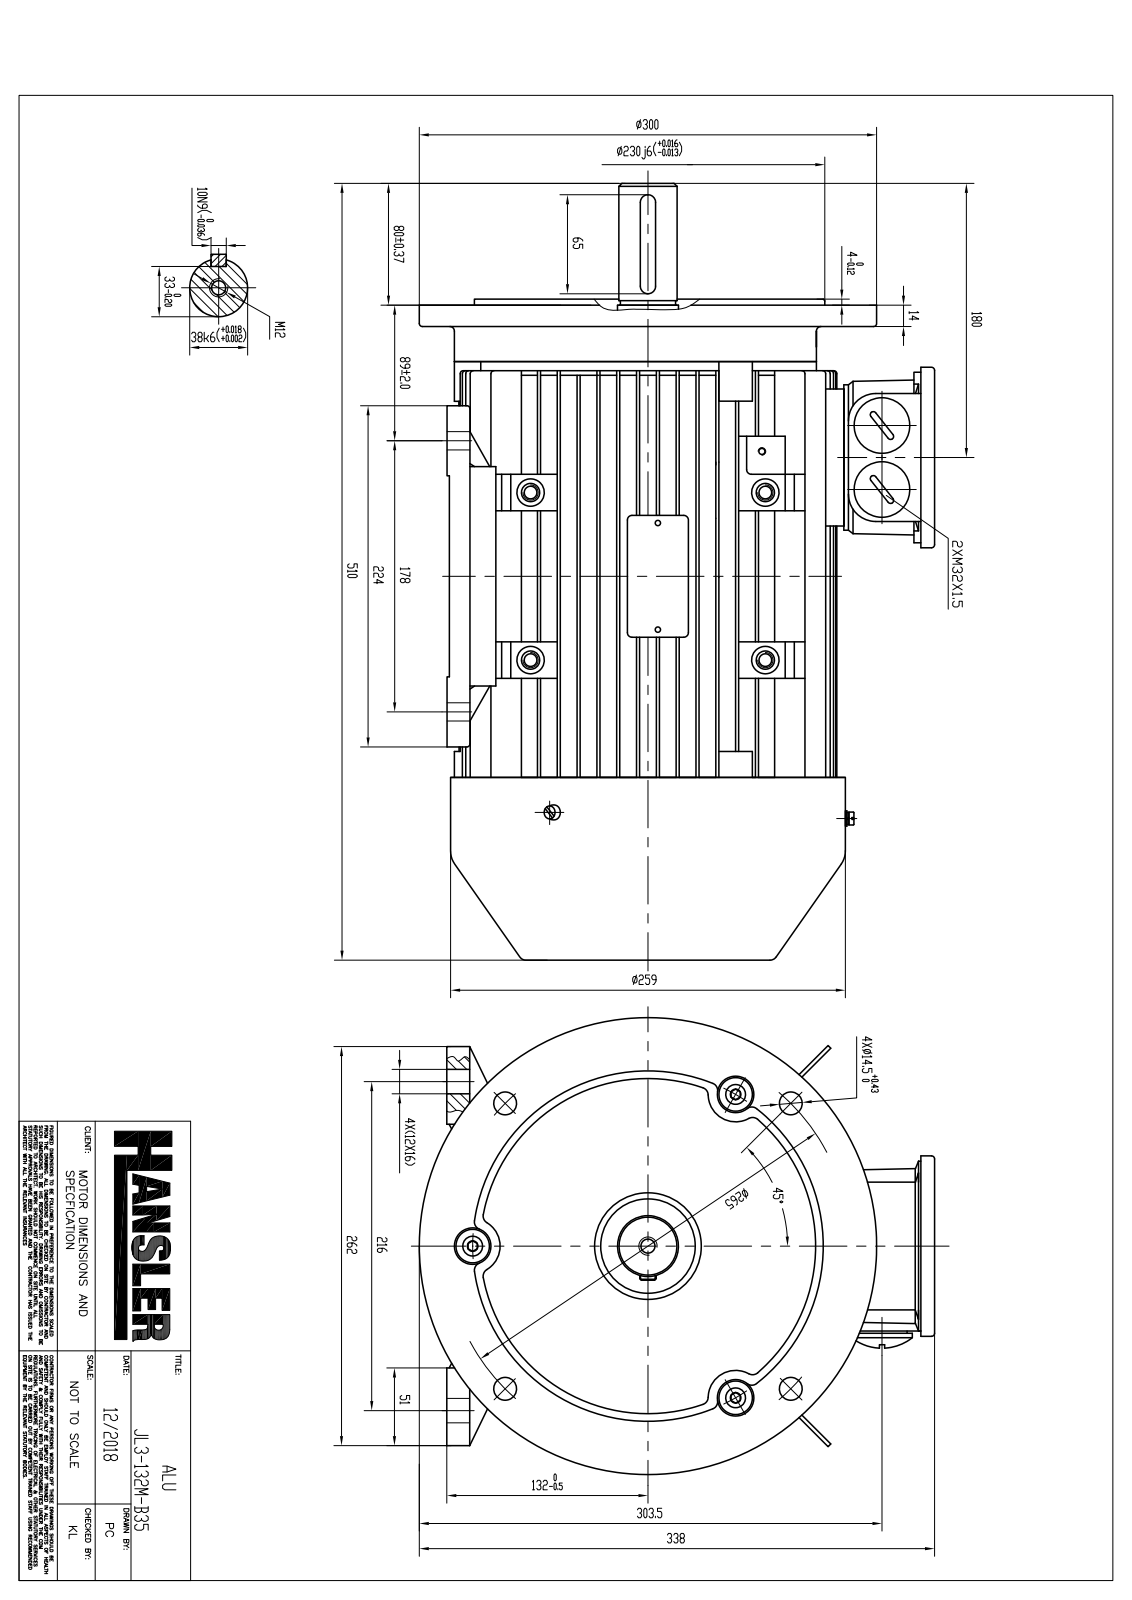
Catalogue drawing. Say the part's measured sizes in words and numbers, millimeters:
The part is named "JL3-132M-B35". Its 3-D file was written by "SolidWorks 2018 (CONFIG_CONTROL_DESIGN)". It is 57 solids with 5351 faces: 2438 planar, 2271 cylindrical and 642 other. Overall it measures 496 by 337.82 by 300 millimeters. Its volume is 3 907 000 cubic millimeters and its surface area 1 878 000 square millimeters. Round holes: 27 of diameter 5, 14 of diameter 10, 12 of diameter 2.92, 8 of diameter 18, 6 of diameter 5.8, 6 of diameter 11, 5 of diameter 5.25, 5 of diameter 5.3, 4 of diameter 2.98, 4 of diameter 5.5, 4 of diameter 8, 4 of diameter 8.5. Round bosses or shafts: 16 of diameter 3.82, 9 of diameter 10, 8 of diameter 16, 8 of diameter 12, 6 of diameter 5.5, 5 of diameter 7.85, 5 of diameter 4.48, 4 of diameter 17. Partial cylindrical surfaces (rounded edges, fillets, slot ends): 816 of radius 0.5, 146 of radius 2, 60 of radius 5, 56 of radius 3, 36 of radius 1, 26 of radius 4, 18 of radius 2.5, 12 of radius 0.2. The main face-to-face distances are 13, 2, 26, 11, 91, 104, 15, 78, 39, 24. The hole center spacings are 84.34, 10.4, 144.72, 21.21, 68, 117.38, 7.23, 12.67.
